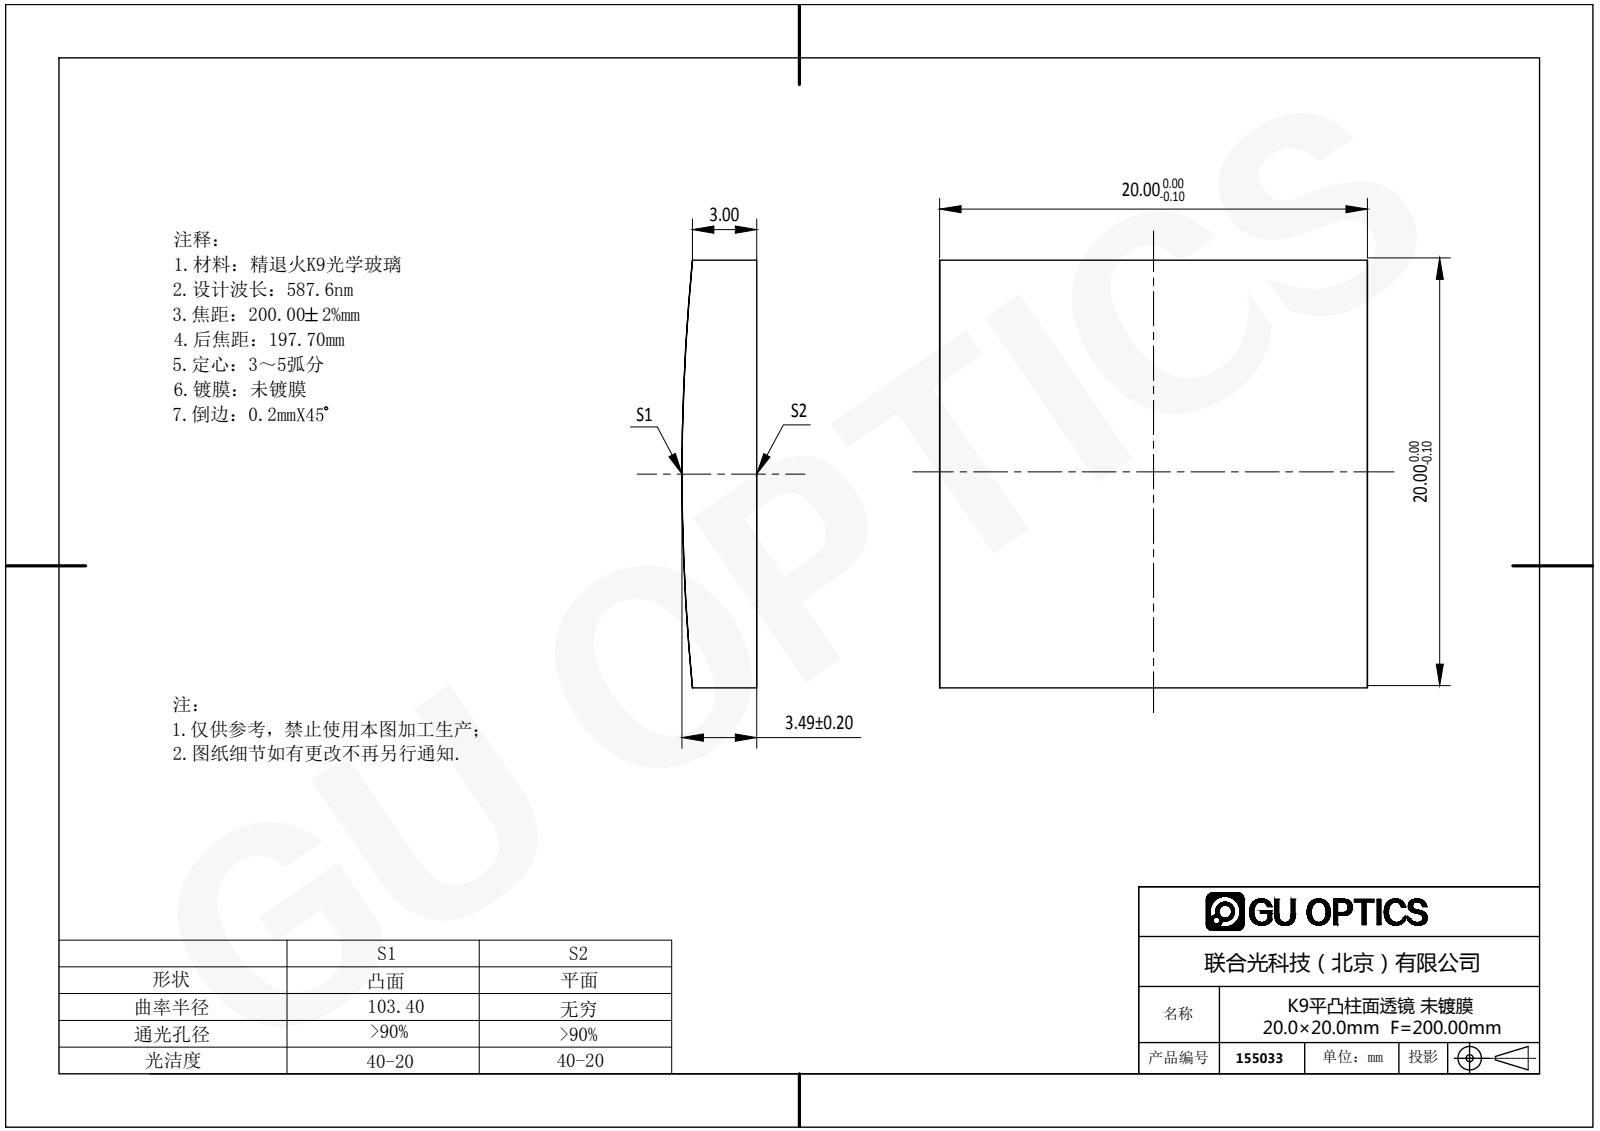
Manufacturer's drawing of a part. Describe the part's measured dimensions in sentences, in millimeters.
The part is named "155033". Its 3-D file was written by "SolidWorks 2016 (AUTOMOTIVE_DESIGN)". It is 1 solid with 6 faces: 5 planar, 1 cylindrical and 0 other. Overall it measures 20 by 20 by 3.49 millimeters. Its volume is 1 331 cubic millimeters and its surface area 1 054 square millimeters. Partial cylindrical surfaces (rounded edges, fillets, slot ends): 1 of radius 103.4. The main face-to-face distances are 20.
